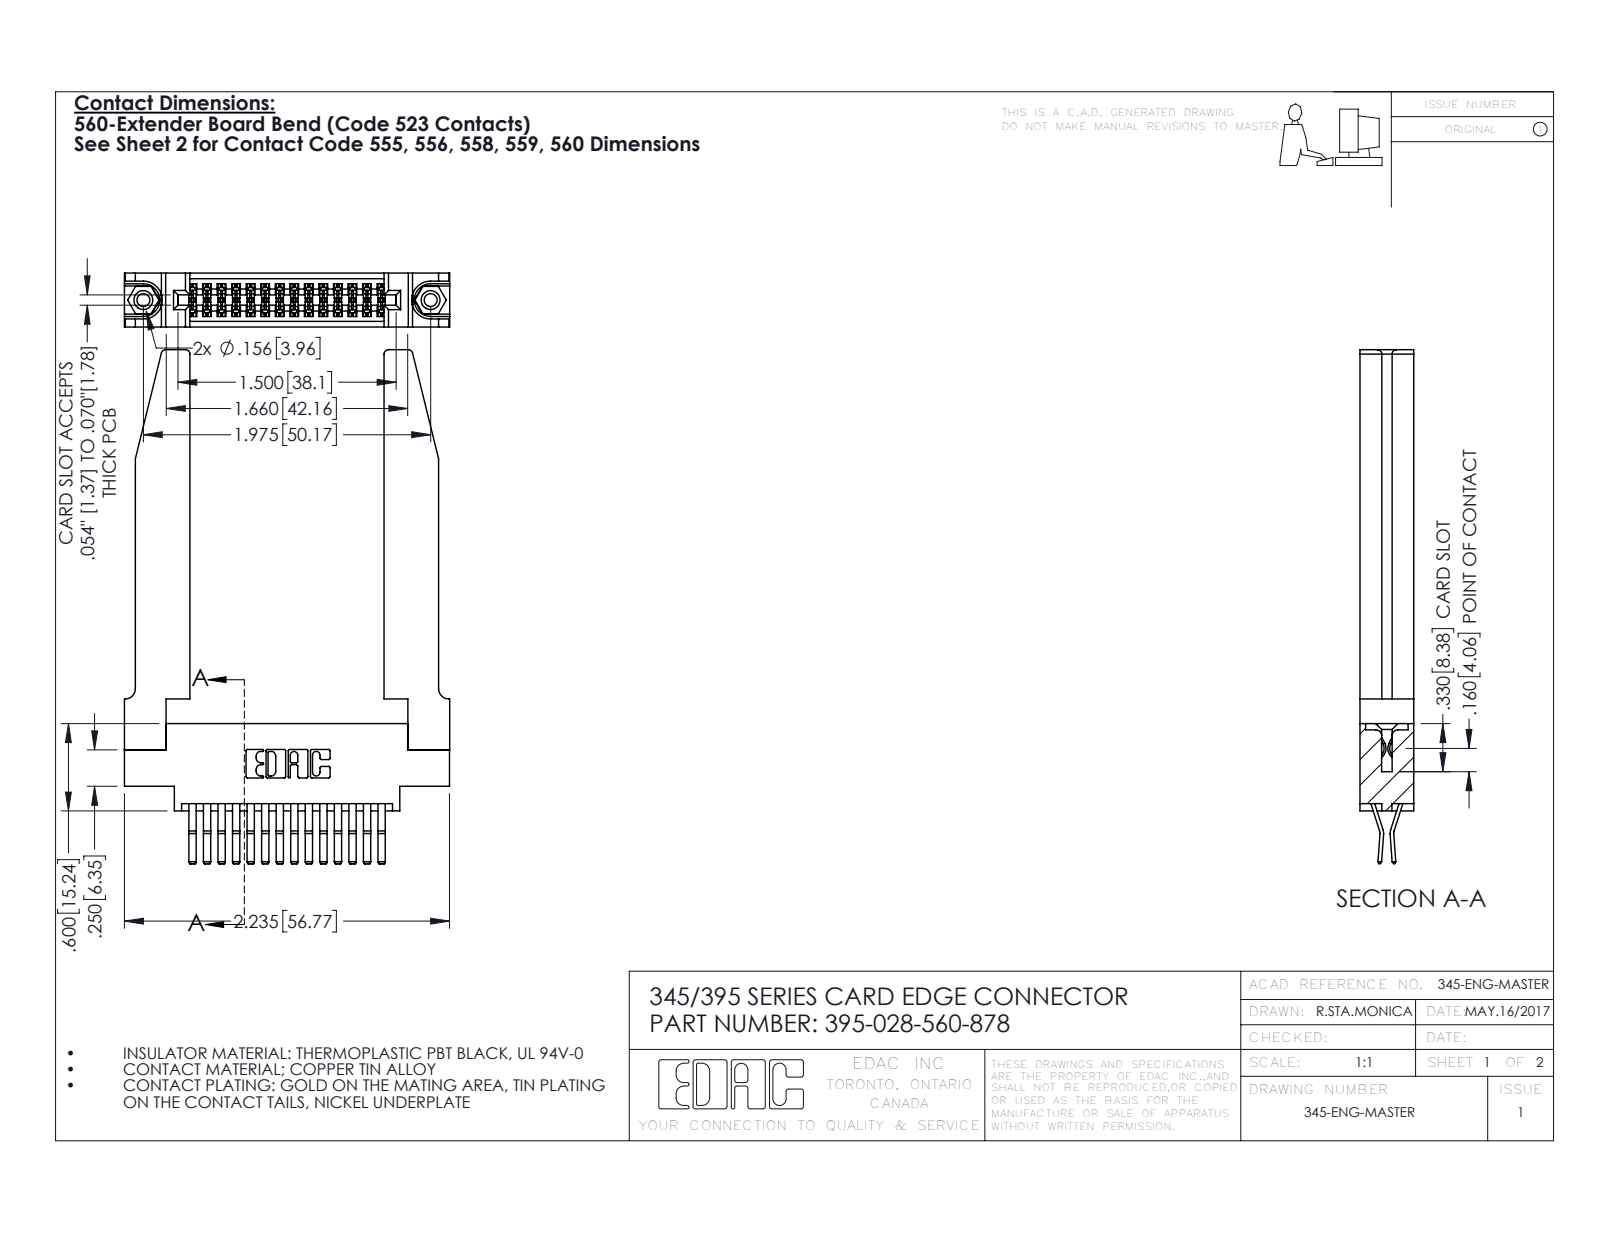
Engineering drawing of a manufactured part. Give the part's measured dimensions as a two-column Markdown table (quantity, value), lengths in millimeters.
| quantity | value |
| --- | --- |
| part name | 395-028-560-878; 345 Part_0.170 Offset - 0.156 Dia-TH; 345-220-078_345-220-078; 345-292-001_560 Tail (+1 more) |
| STEP written by | SolidWorks 2016 (CONFIG_CONTROL_DESIGN) |
| units | millimeters |
| bodies | 33 solids, 1820 faces (1150 planar, 618 cylindrical, 52 other) |
| overall size | 89.7 × 56.8 × 9.4 |
| volume | 13 100 mm³ |
| surface area | 14 790 mm² |
| round holes (diameter × count) | 2.3 × 2, 3.2 × 2, 4 × 2, 1.6 × 1 |
| round bosses / shafts (diameter × count) | 3.9 × 2 |
| partial cylindrical surfaces (radius × count) | 0.2 × 43, 0.3 × 22, 0.8 × 8, 0.2 × 6, 0.8 × 6, 0.7 × 3, 0.3 × 2, 0.4 × 2 |
| main face-to-face distances | 9.4, 1.8, 7.6, 0.6, 3.8, 3.8, 5.1, 5.6, 2, 3.1 |
| hole center spacings | 6.9, 44.2, 50.2 |
